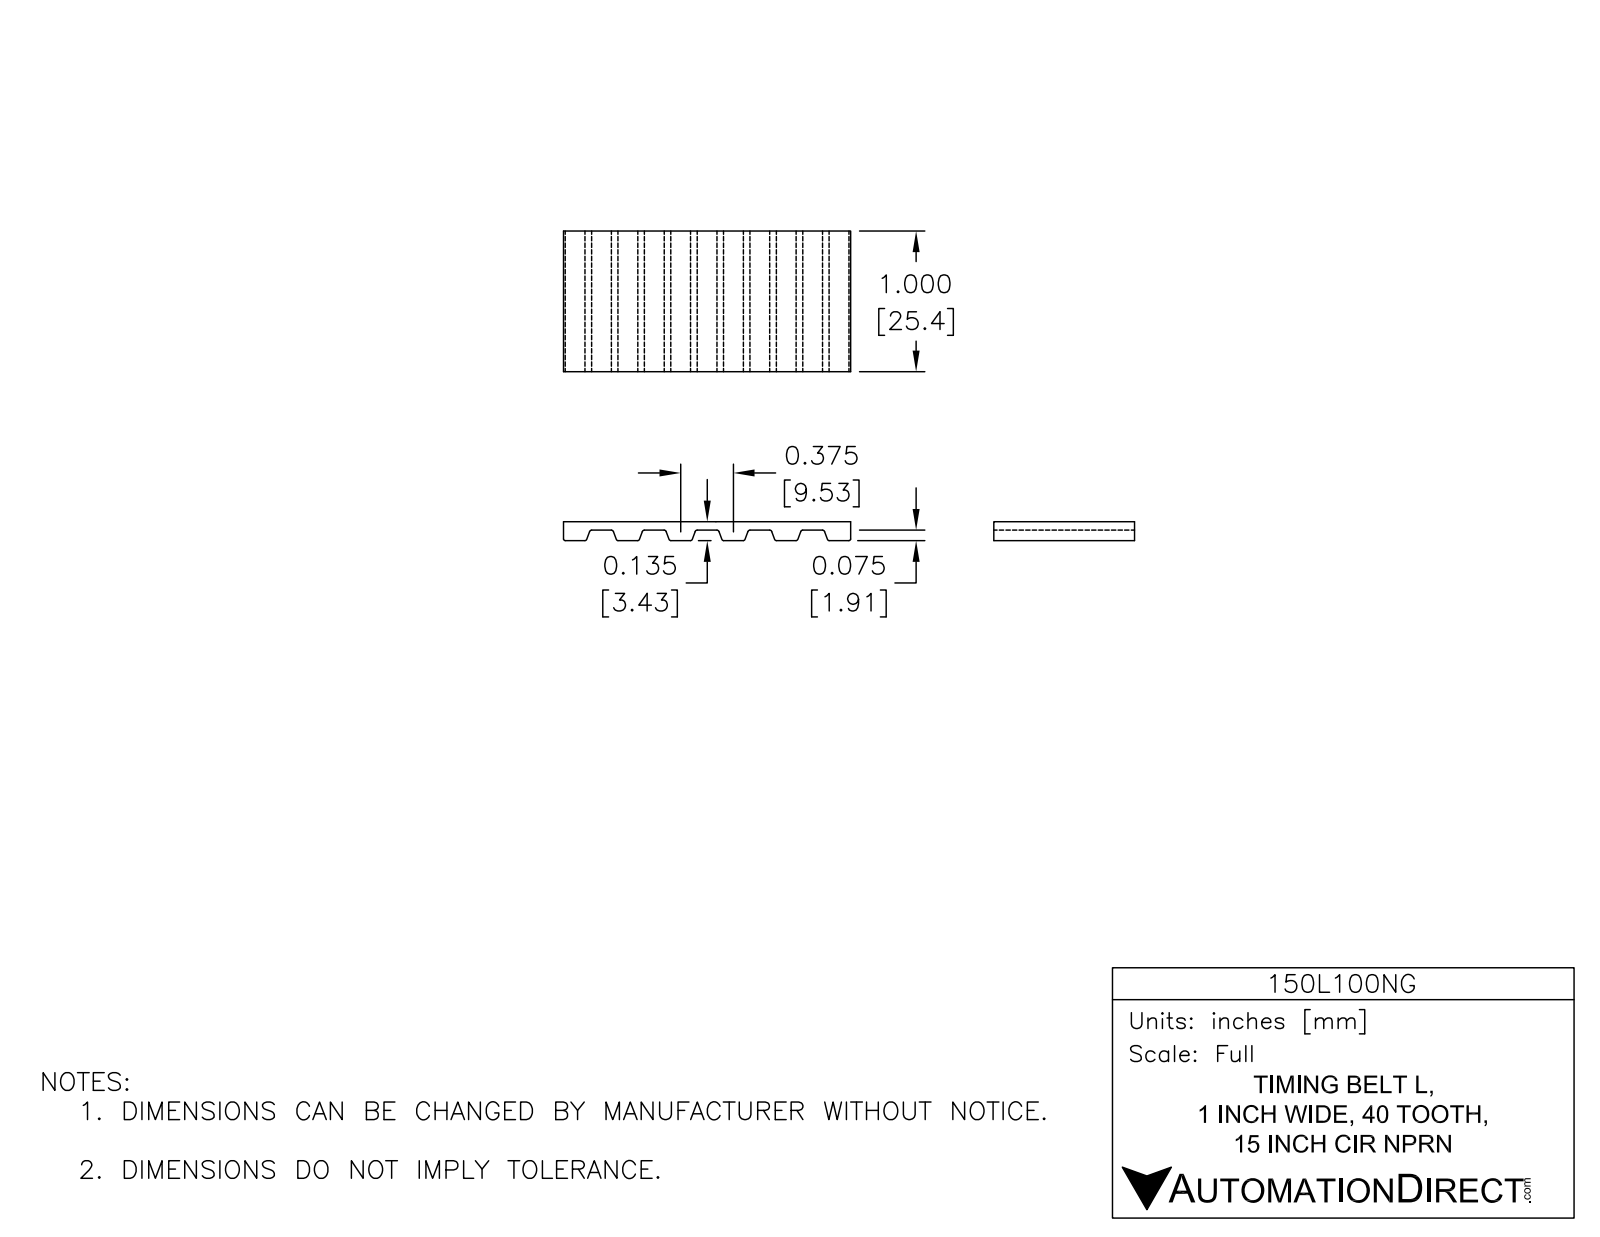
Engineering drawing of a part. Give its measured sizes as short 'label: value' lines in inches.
name: 150L100NG
written by: SolidWorks 2014 (AUTOMOTIVE_DESIGN)
unit: in
bodies: 1 solid, 334 faces (136 planar, 198 cylindrical, 0 other)
size: 5.788 × 3 × 1
volume: 1.342 in³; area: 35.79 in²
rounds: 156× R0.02, 2× R1.435, 2× R1.5
face distances: 0.065, 2.935, 3, 1, 2.87, 0.14, 2.86, 0.075, 2.795, 0.352
